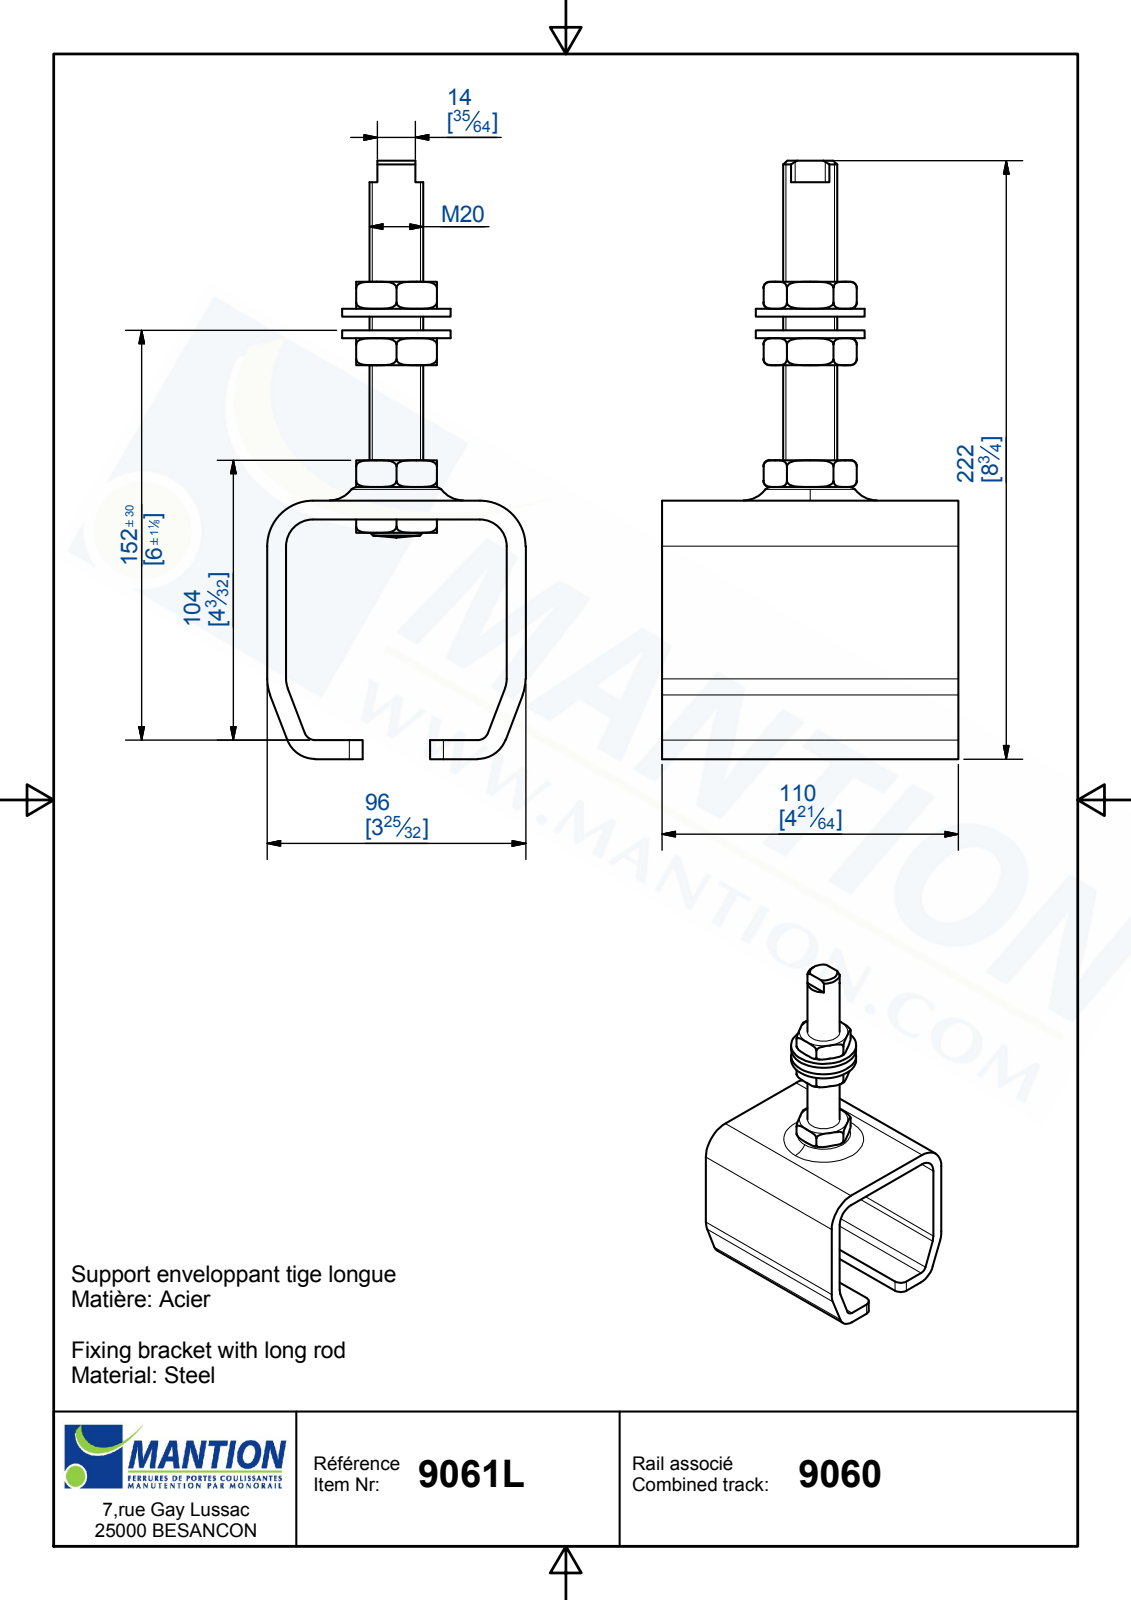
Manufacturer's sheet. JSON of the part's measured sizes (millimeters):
{"part_name": "9061L; 15995; PT8571L; 14980 (+2 more)", "step_written_by": "Autodesk Inventor 2017 (AUTOMOTIVE_DESIGN)", "units": "millimeters", "bodies": {"solids": 8, "faces": 154, "planar": 68, "cylindrical": 32, "other": 54}, "overall_size": [222.24, 110, 96], "volume_mm3": 301632, "surface_area_mm2": 97134, "round_holes": [[17.29, 1], [20.1, 1], [21, 1]], "round_bosses_or_shafts": [[40.3, 1], [20, 1]], "partial_cylinders_radius": [[4, 8], [5, 4], [10, 4], [17, 4], [11, 2]], "face_to_face_distances": [7, 89, 82, 96, 5, 8, 110, 30, 3, 70.24]}
